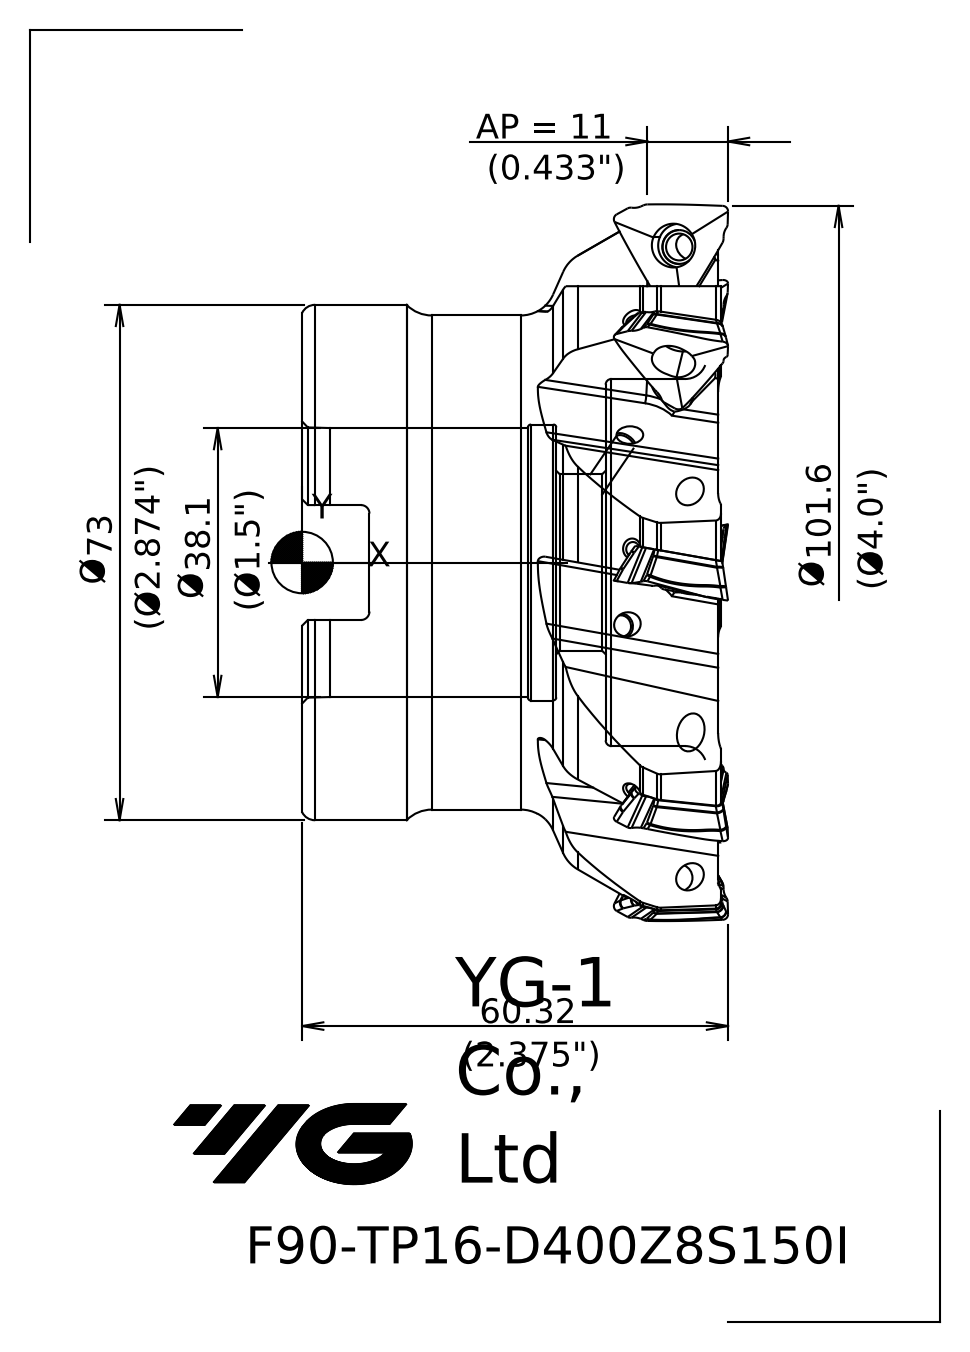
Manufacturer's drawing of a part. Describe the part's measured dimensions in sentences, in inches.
The part is named "1022C79461C3qzqx". Its 3-D file was written by "SIEMENS PLM Software NX 10.0 (AP203_CONFIGURATION_CONTROLLED_3D_DESIGN_OF_MECHANICAL_PARTS_AND_ASSEMBLIES_MIM_LF)". It is 2 solids with 312 faces: 22 planar, 11 cylindrical and 279 other. Overall it measures 4.005 by 4.005 by 2.375 inches. Its volume is 13.38 cubic inches and its surface area 75.59 square inches. Round holes: 1 of diameter 0.205, 1 of diameter 0.984, 1 of diameter 1.5, 1 of diameter 1.539, 1 of diameter 2.047. Round bosses or shafts: 1 of diameter 2.874, 1 of diameter 2.756. Partial cylindrical surfaces (rounded edges, fillets, slot ends): 2 of radius 0.047. The main face-to-face distances are 2.32, 0.627, 1.693, 0.903, 0.276, 1.417, 1.944, 1.317, 1.042, 0.376.
